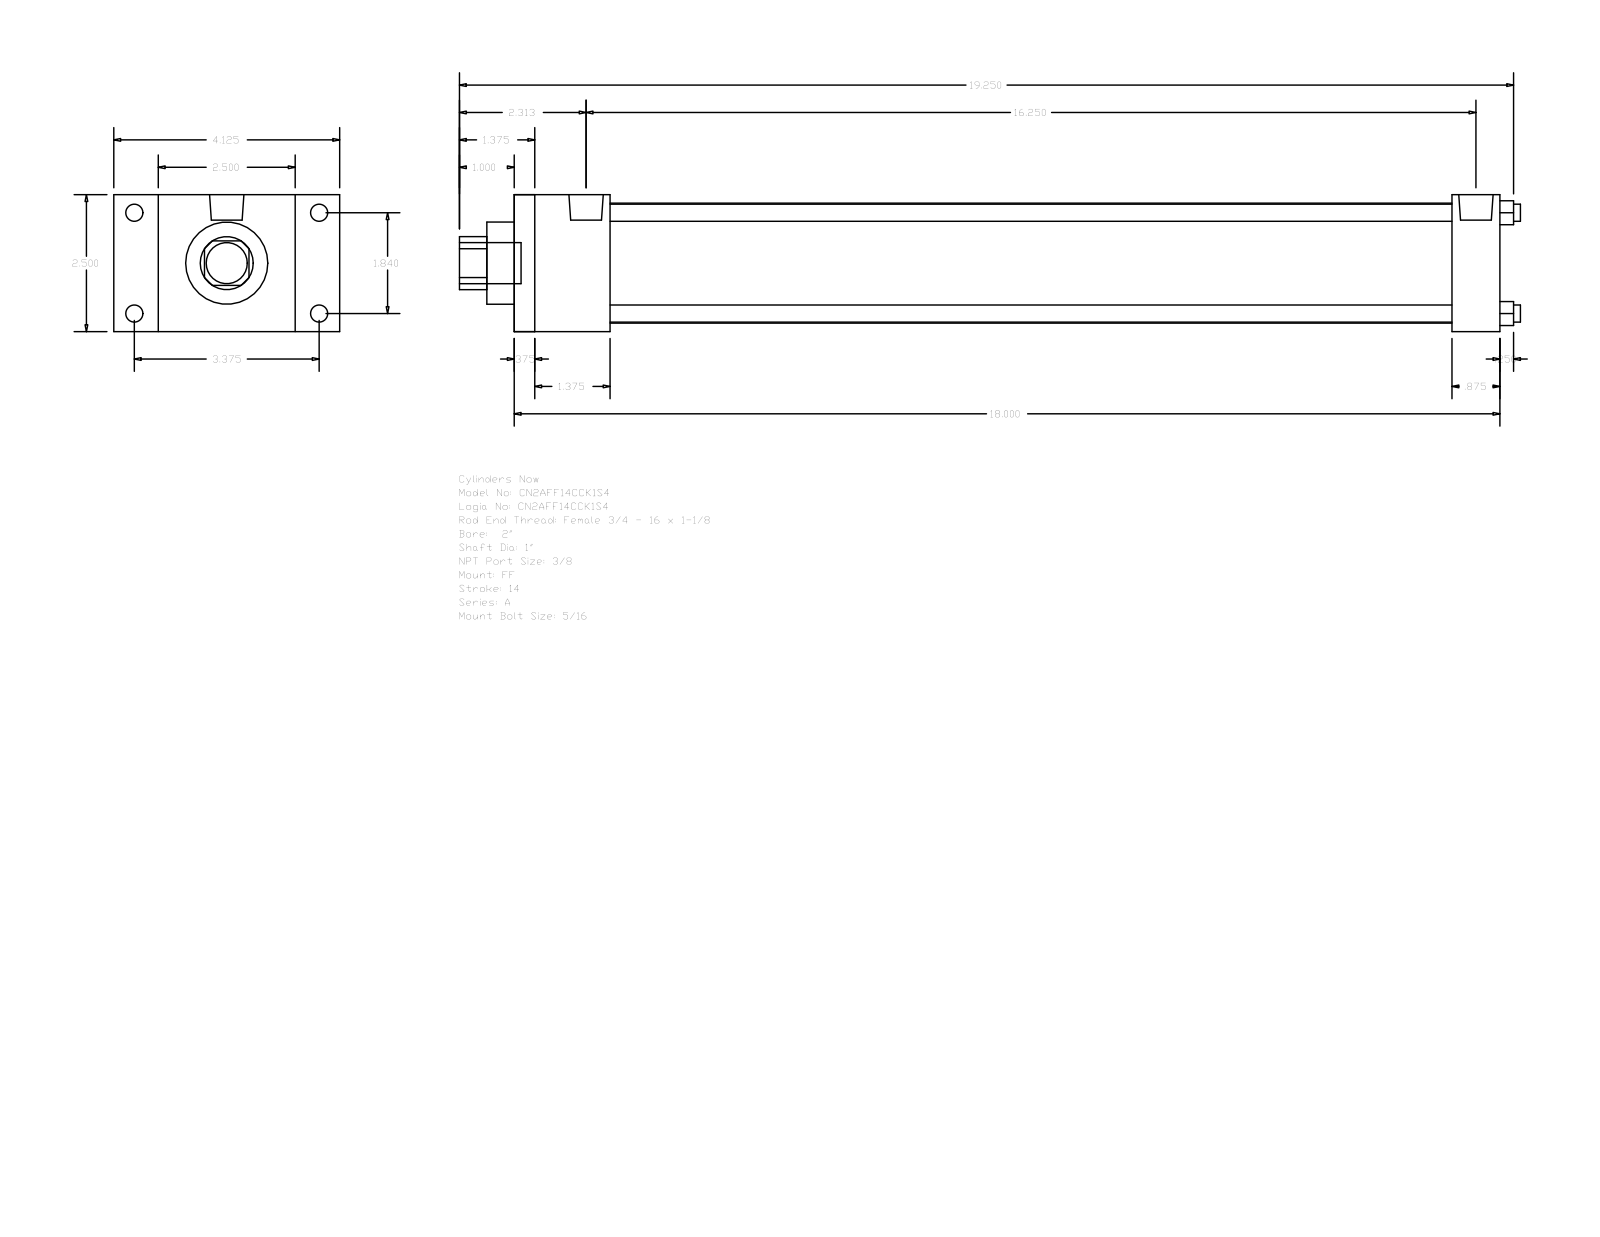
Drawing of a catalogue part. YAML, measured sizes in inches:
part_name: "A_FF__0200_1"
step_written_by: "GSSL Pune (CONFIG_CONTROL_DESIGN)"
units: inches
bodies: {solids: 0, faces: 92, planar: 64, cylindrical: 28, other: 0}
overall_size: [19.375, 4.125, 2.5]
round_holes:
  - {diameter: 0.313, count: 4}
  - {diameter: 1, count: 1}
  - {diameter: 1.5, count: 1}
  - {diameter: 2.19, count: 1}
round_bosses_or_shafts:
  - {diameter: 0.313, count: 4}
  - {diameter: 0.219, count: 4}
  - {diameter: 0.627, count: 2}
  - {diameter: 0.75, count: 1}
partial_cylinders:
  - {radius: 0.484, count: 1}
face_to_face_distances: [2.5, 18, 17.625, 0.375, 0.875, 0.813, 1.75, 17.125, 1.375, 16.75]
hole_center_spacings: [1.301, 1.84, 2.602]
